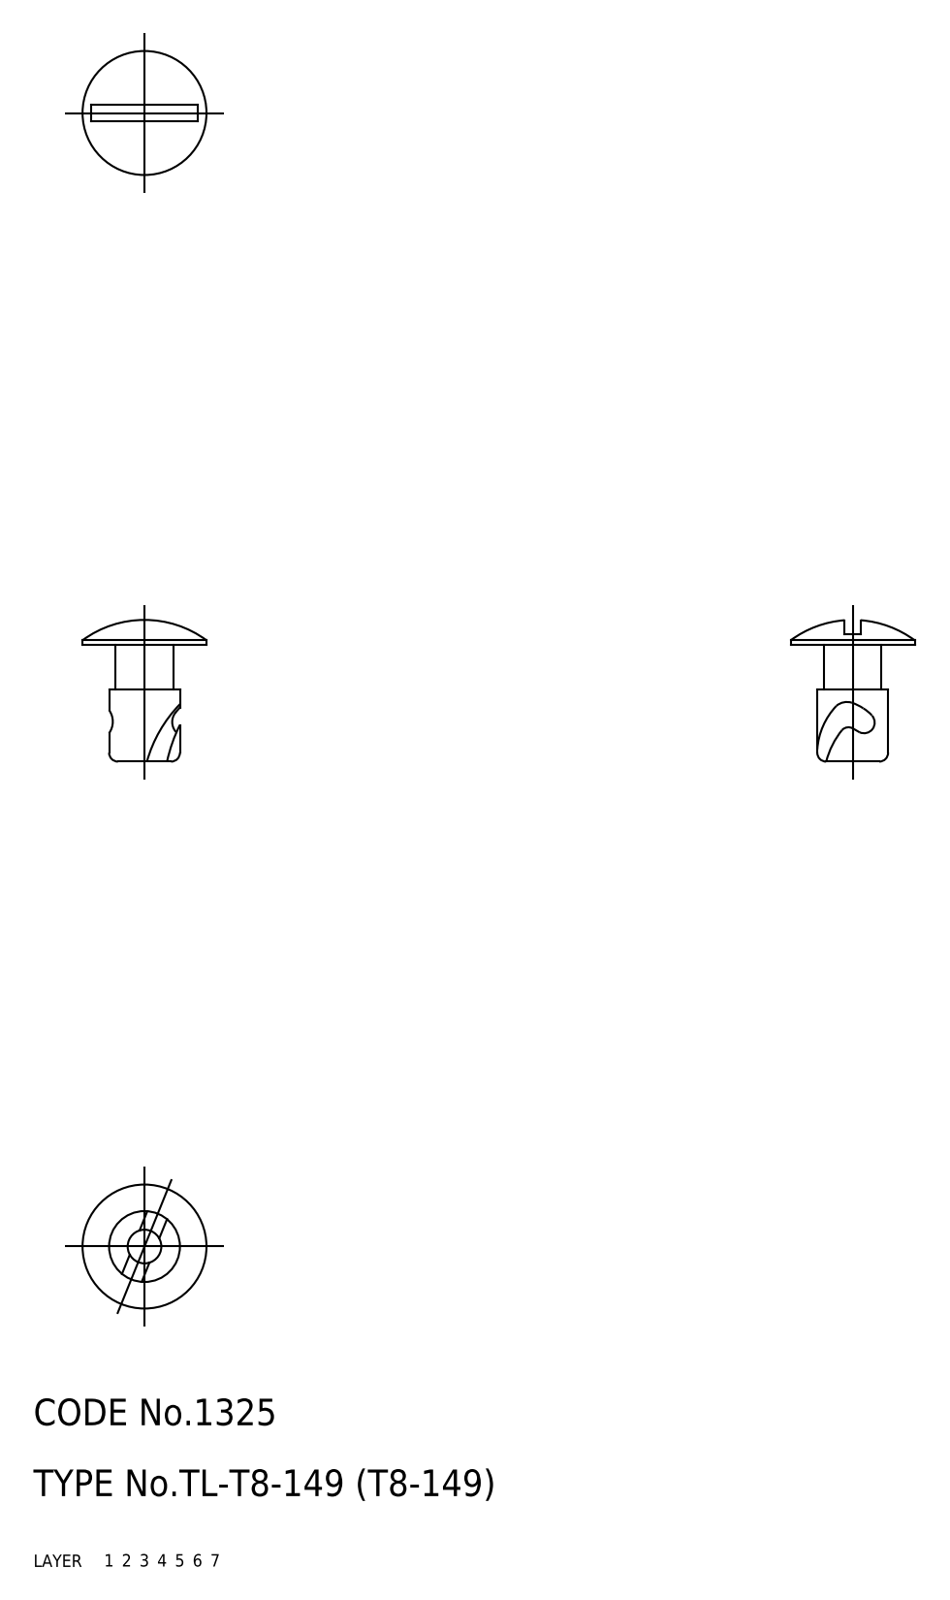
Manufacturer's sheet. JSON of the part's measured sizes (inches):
{"part_name": "67112835", "step_written_by": "CADfix (AUTOMOTIVE_DESIGN)", "units": "inches", "bodies": {"solids": 1, "faces": 35, "planar": 0, "cylindrical": 0, "other": 35}, "overall_size": [0.629, 0.551, 0.551], "volume_in3": 0.039, "surface_area_in2": 1.22}
